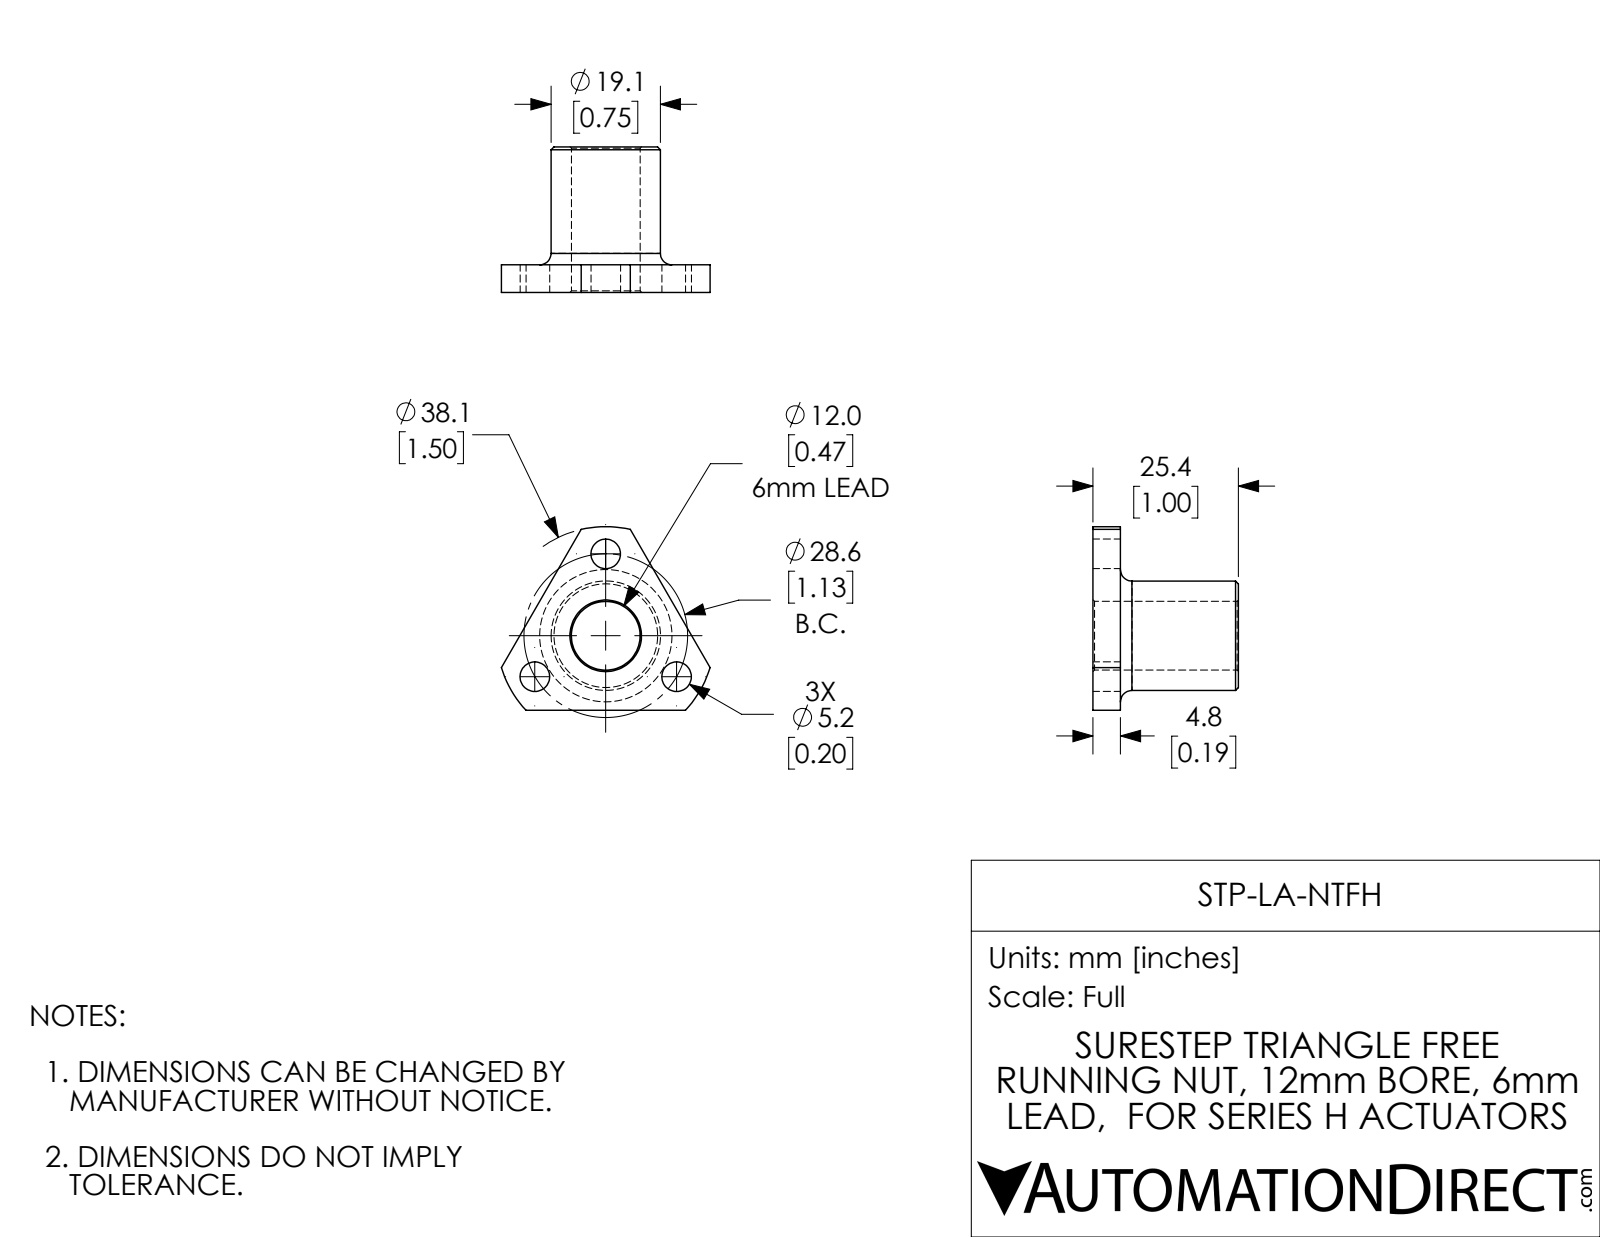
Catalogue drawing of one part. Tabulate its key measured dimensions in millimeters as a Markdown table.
| quantity | value |
| --- | --- |
| part name | STP-LA-NTFH |
| STEP written by | SolidWorks 2017 (AUTOMOTIVE_DESIGN) |
| units | millimeters |
| bodies | 1 solid, 27 faces (6 planar, 13 cylindrical, 8 other) |
| overall size | 36.44 × 32.05 × 25.4 |
| volume | 6 570 mm³ |
| surface area | 4 103 mm² |
| round holes (diameter × count) | 5.16 × 3, 12 × 1 |
| round bosses / shafts (diameter × count) | 19.1 × 1 |
| partial cylindrical surfaces (radius × count) | 19.05 × 1 |
| main face-to-face distances | 4.8, 20.6, 25.4 |
| hole center spacings | 14.29, 24.76, 14.3, 24.75 |
